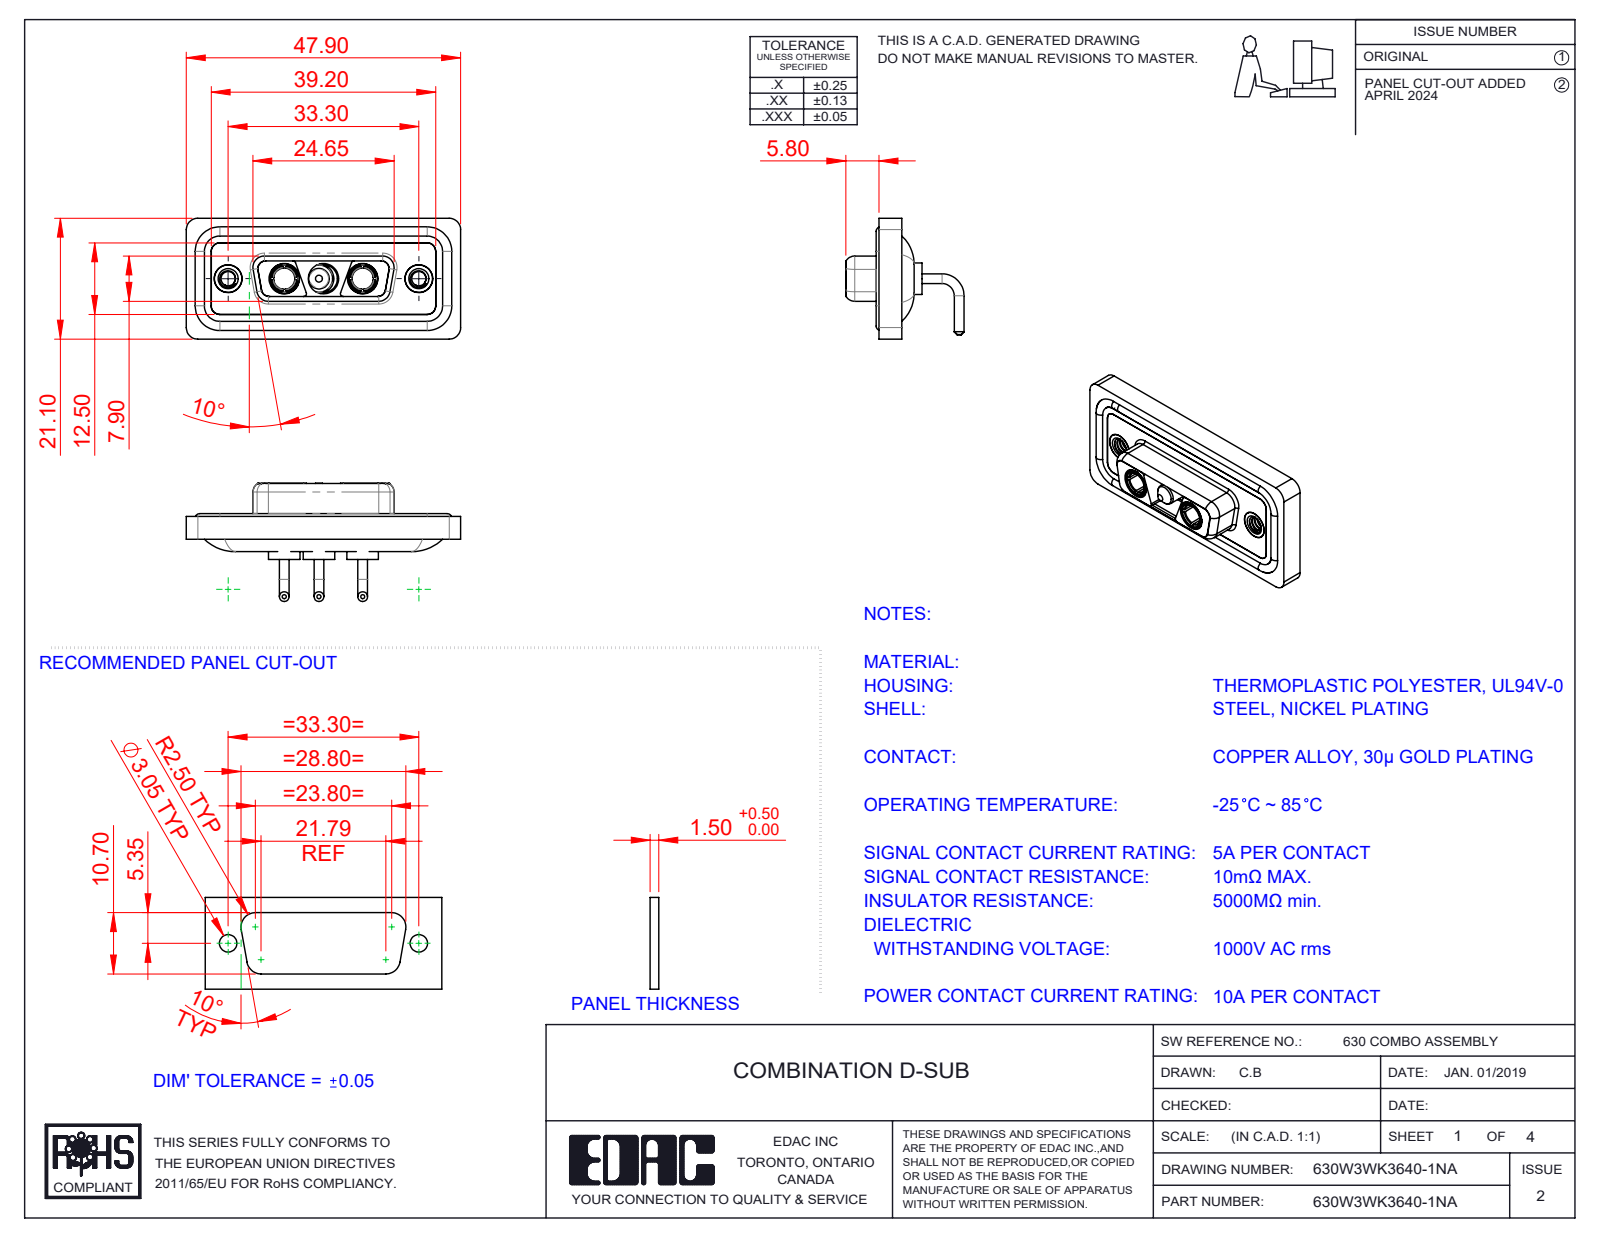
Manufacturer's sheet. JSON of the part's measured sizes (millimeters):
{"part_name": "630Combo Shell Front_15 Contacts; Power Pin_10A RA; 630Combo Threaded Rivet_A; 630Combo Shell Rear_15 Contacts (+4 more)", "step_written_by": "SolidWorks 2023 (CONFIG_CONTROL_DESIGN)", "units": "millimeters", "bodies": {"solids": 13, "faces": 589, "planar": 178, "cylindrical": 262, "other": 149}, "overall_size": [47.9, 21.1, 20.65], "volume_mm3": 5851, "surface_area_mm2": 9589, "round_holes": [[4.85, 5], [5.3, 3], [2.5, 2], [3.7, 2], [4, 2], [4.05, 2], [5, 2]], "round_bosses_or_shafts": [[1.7, 6], [1.6, 4], [5.5, 3], [5.2, 3], [4.75, 3], [3.75, 3], [4.96, 2], [4.95, 2]], "partial_cylinders_radius": [[2, 20], [1.5, 18], [1.35, 12], [0.5, 8], [1.6, 8], [0.25, 4], [0.6, 4], [0.65, 4]], "face_to_face_distances": [0.4, 1.8, 1.1, 1.6, 2.9, 2.5, 3.1, 3.7, 1.5, 4.1], "hole_center_spacings": [6.85, 9.8, 16.65, 23.5, 13.7, 33.3]}
